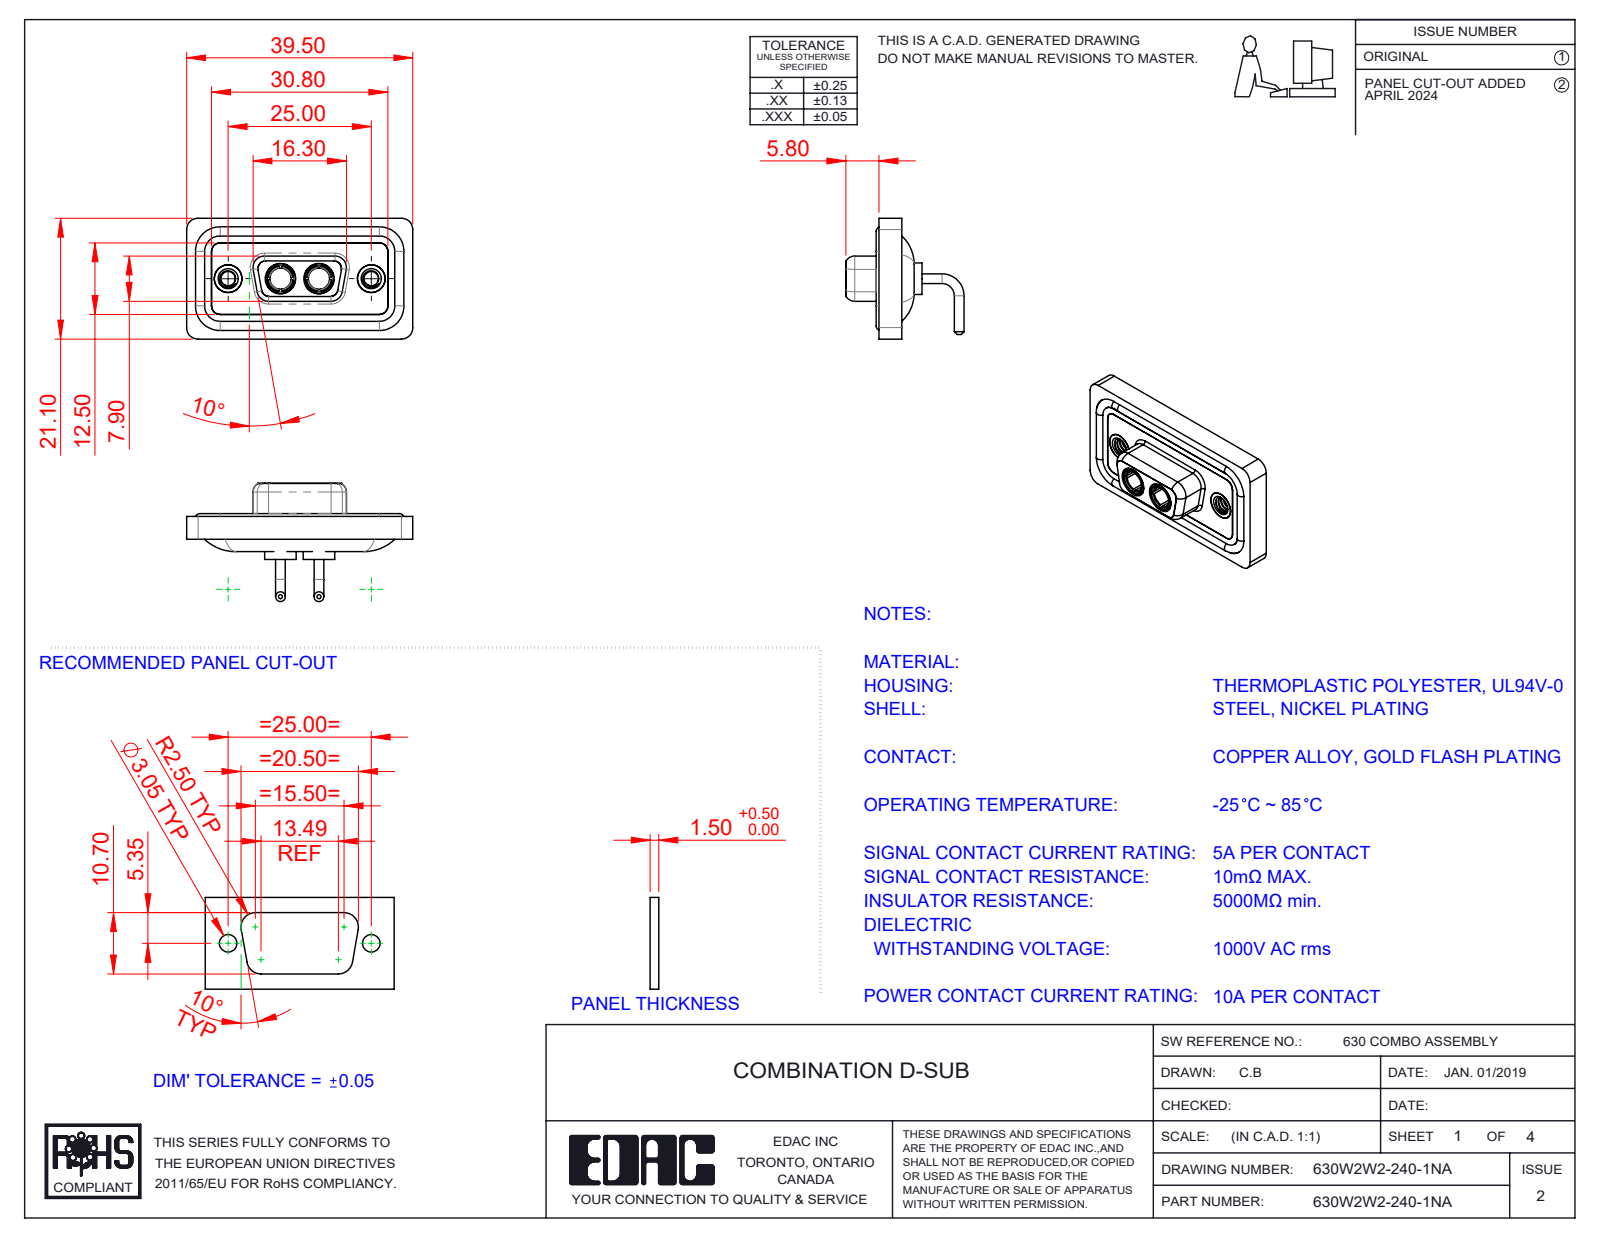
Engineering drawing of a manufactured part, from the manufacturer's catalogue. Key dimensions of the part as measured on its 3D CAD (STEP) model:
Part name (STEP PRODUCT): 630Combo Threaded Rivet_A; 630Combo Shell Rear_09 Contacts; 630Combo Housing_2W2; 630W2W2-140-1NA (+3 more)
STEP written by: SolidWorks 2023 (CONFIG_CONTROL_DESIGN)
Units: millimetres
Bodies: 11 solids, 536 faces (163 planar, 236 cylindrical, 137 other)
Overall size (bounding box): 39.5 × 21.1 × 20.65
Volume: 4 693 mm³ · Surface area: 7 687 mm²
Round holes (diameter × count): ⌀4.85 ×4, ⌀2.5 ×2, ⌀3.7 ×2, ⌀4 ×2, ⌀4.05 ×2, ⌀5 ×2, ⌀5.3 ×2
Round bosses / shafts (diameter × count): ⌀1.7 ×4, ⌀1.6 ×4, ⌀5.5 ×2, ⌀5.2 ×2, ⌀4.96 ×2, ⌀4.95 ×2, ⌀4.8 ×2, ⌀4.75 ×2
Partial cylindrical surfaces — rounded edges, fillets, slot ends (radius × count): R1.5 ×18, R2 ×18, R1.35 ×8, R1.6 ×8, R0.25 ×4, R0.5 ×4, R0.6 ×4, R0.65 ×4
Main face-to-face distances: 0.4, 1.8, 1.1, 2.9, 2.5, 1.6, 3.1, 1.5, 2.1, 4
Hole centre spacings: 9.14, 15.86, 6.72, 25
